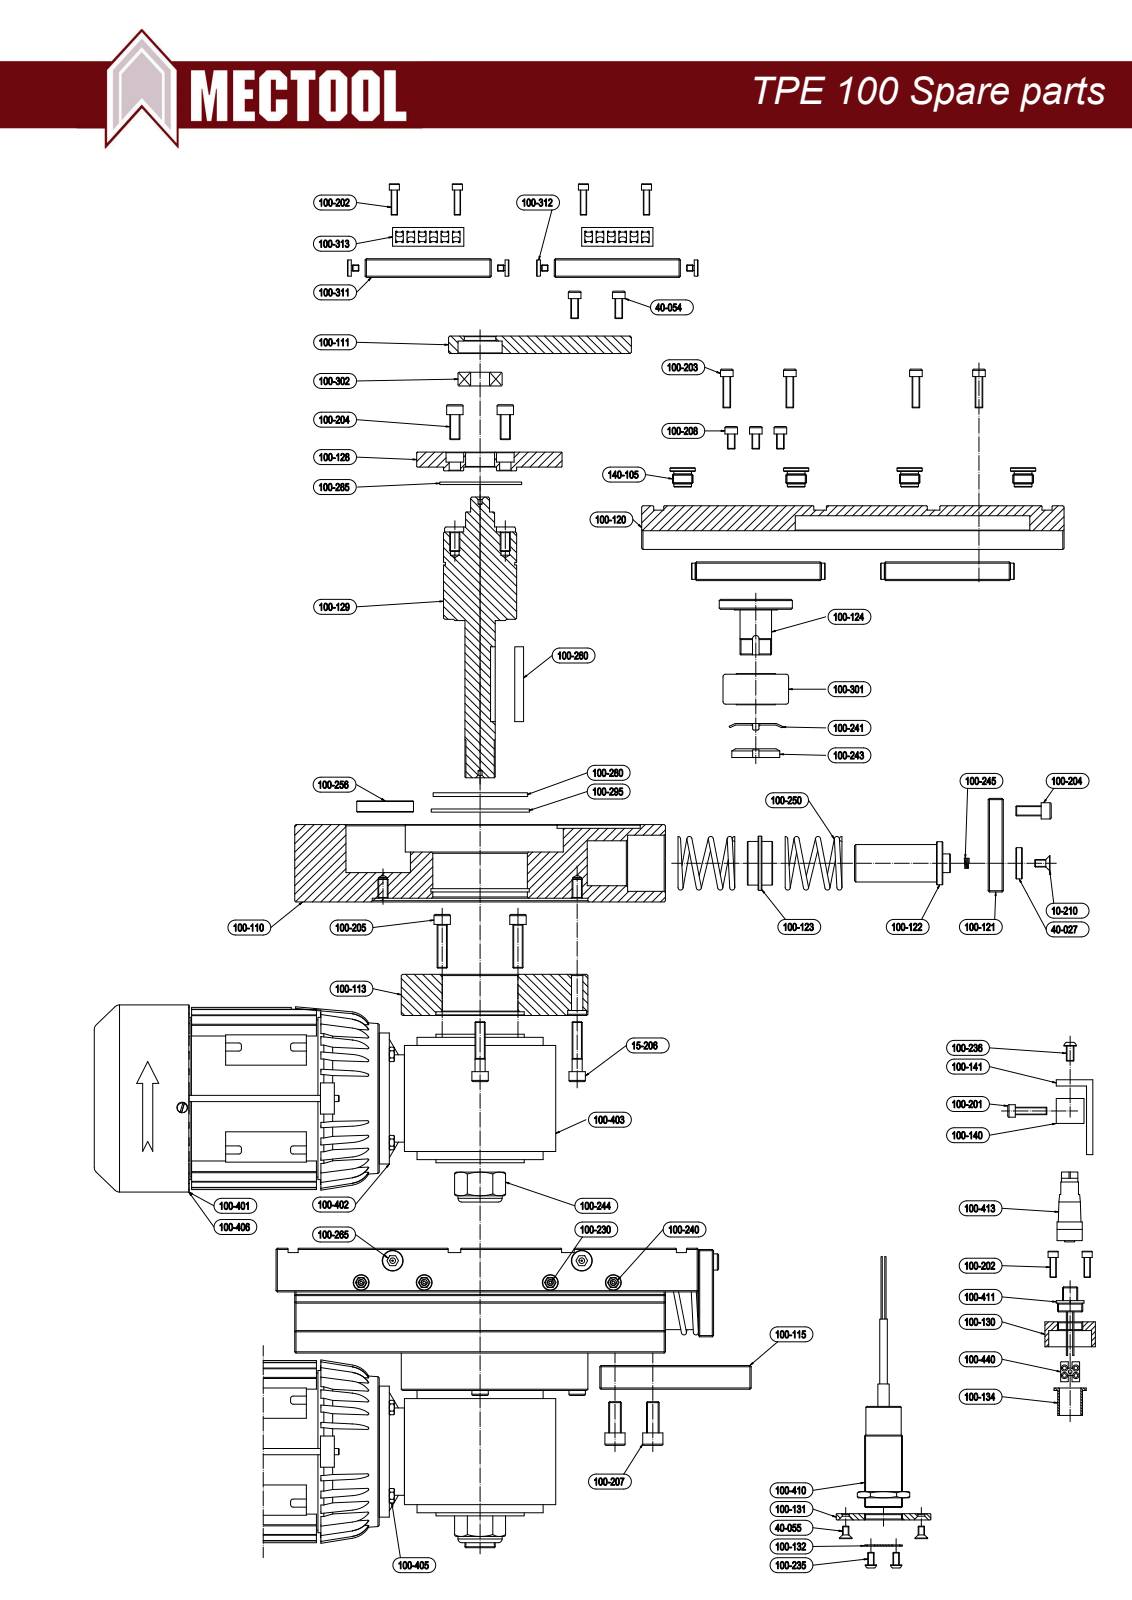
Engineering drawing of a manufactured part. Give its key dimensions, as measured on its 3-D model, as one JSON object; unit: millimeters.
{"step_written_by": "Spatial InterOp 3D (automotive_design)", "units": "millimeters", "bodies": {"solids": 107, "faces": 2346, "planar": 1989, "cylindrical": 161, "other": 196}, "overall_size": [525, 344, 241], "volume_mm3": 11470000, "surface_area_mm2": 1040000, "round_holes": [[11, 14], [2.5, 8], [20, 8], [12, 5], [4, 4], [10, 3], [13, 3], [15, 3], [40, 3], [9, 2], [5.25, 1], [8, 1]], "round_bosses_or_shafts": [[6, 18], [10, 14], [8, 12], [13, 6], [26, 3], [120, 2], [4, 2], [150, 1]], "partial_cylinders_radius": [[5, 4], [8, 4], [6.5, 2], [7, 2], [20, 2], [15, 1]], "face_to_face_distances": [22, 81, 20, 2, 84, 64, 83, 19, 61, 59], "hole_center_spacings": [150, 57.87, 90, 174.93, 176.77, 200, 50, 18.68]}
